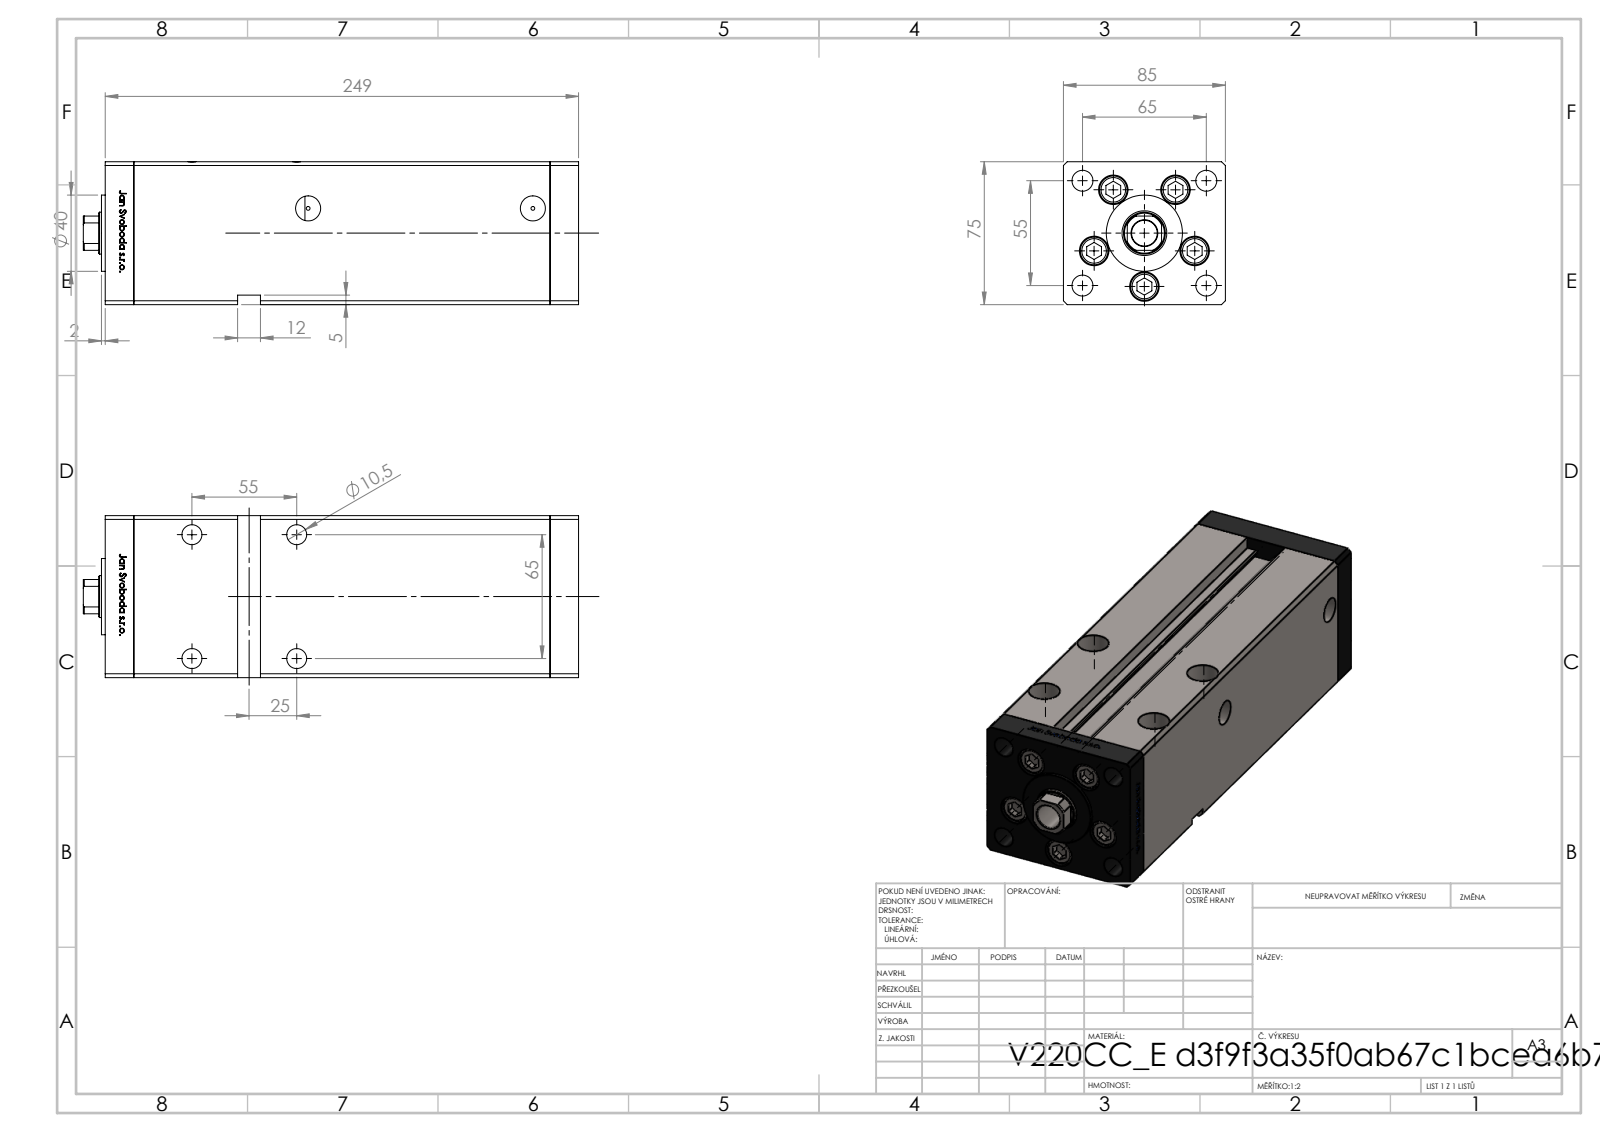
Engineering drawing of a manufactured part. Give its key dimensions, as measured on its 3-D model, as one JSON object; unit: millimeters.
{"part_name": "V220C_E MIDDLE; V220C_VC_E; V220C_FRONT_E; V220C BACK_E (+1 more)", "step_written_by": "SolidWorks 2019 (CONFIG_CONTROL_DESIGN)", "units": "millimeters", "bodies": {"solids": 14, "faces": 1214, "planar": 475, "cylindrical": 165, "other": 574}, "overall_size": [260, 85, 75], "volume_mm3": 1341000, "surface_area_mm2": 209201, "round_holes": [[11, 9], [15.5, 5], [10.5, 4], [16.5, 4], [2, 2], [13.16, 2], [13.5, 1], [22, 1], [23.5, 1]], "round_bosses_or_shafts": [[14.5, 5], [8, 5], [40, 1]], "partial_cylinders_radius": [[0.93, 2], [10.5, 1]], "face_to_face_distances": [85, 75, 15, 218.5, 233.5, 248.5, 68.5, 10.5, 34.25, 64.5], "hole_center_spacings": [28, 42.57, 55, 65, 85.15, 16.86, 19.17, 32.33]}
